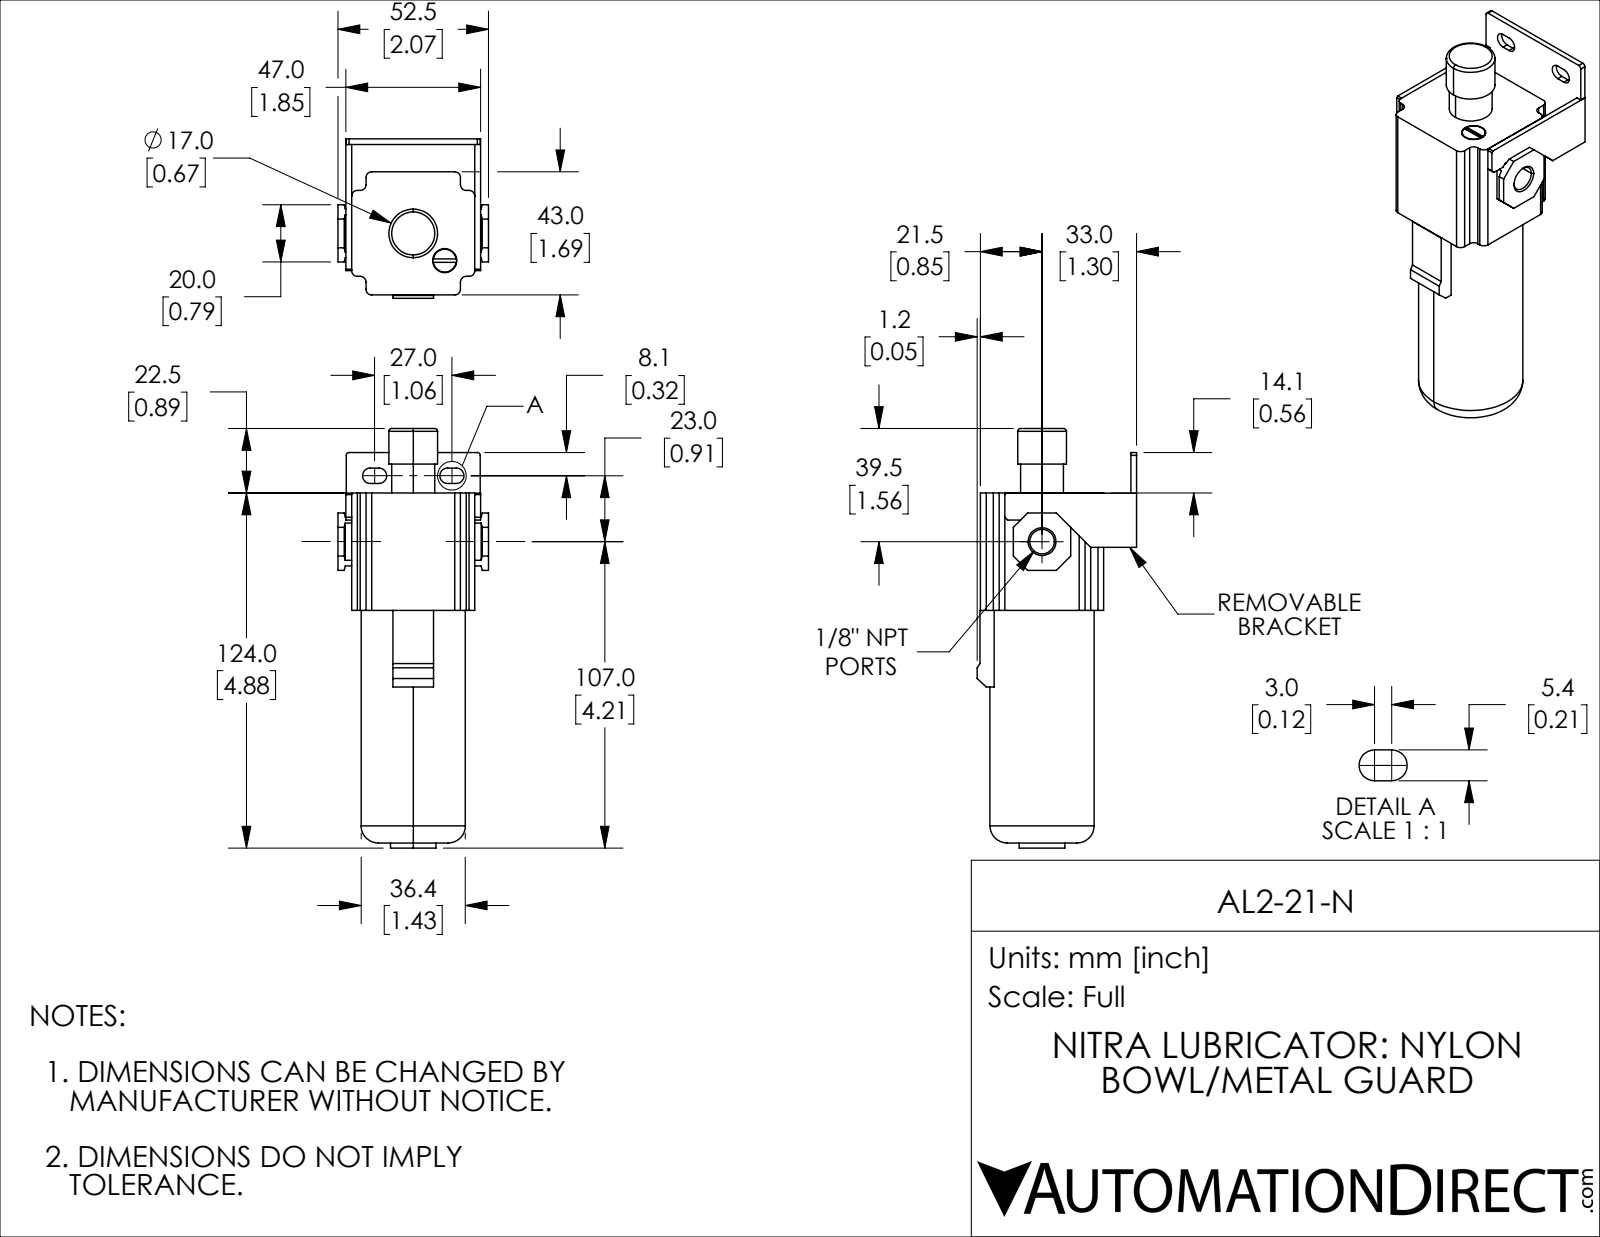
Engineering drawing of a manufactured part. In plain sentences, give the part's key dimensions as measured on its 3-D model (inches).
The part is named "AL2-21-N". Its 3-D file was written by "SolidWorks 2019 (CONFIG_CONTROL_DESIGN)". It is 1 solid with 137 faces: 95 planar, 34 cylindrical and 8 other. Overall it measures 5.768 by 2.192 by 2.067 inches. Its volume is 10.23 cubic inches and its surface area 41.67 square inches. Round holes: 1 of diameter 0.331, 1 of diameter 0.337. Round bosses or shafts: 1 of diameter 1.433, 1 of diameter 0.669, 1 of diameter 0.626, 1 of diameter 0.591, 1 of diameter 0.315. Partial cylindrical surfaces (rounded edges, fillets, slot ends): 12 of radius 0.079, 4 of radius 0.106, 2 of radius 0.039. The main face-to-face distances are 0.079, 1.693, 2.067, 0.453, 1.772, 0.374, 2.146, 1.614, 1.85, 0.108.
